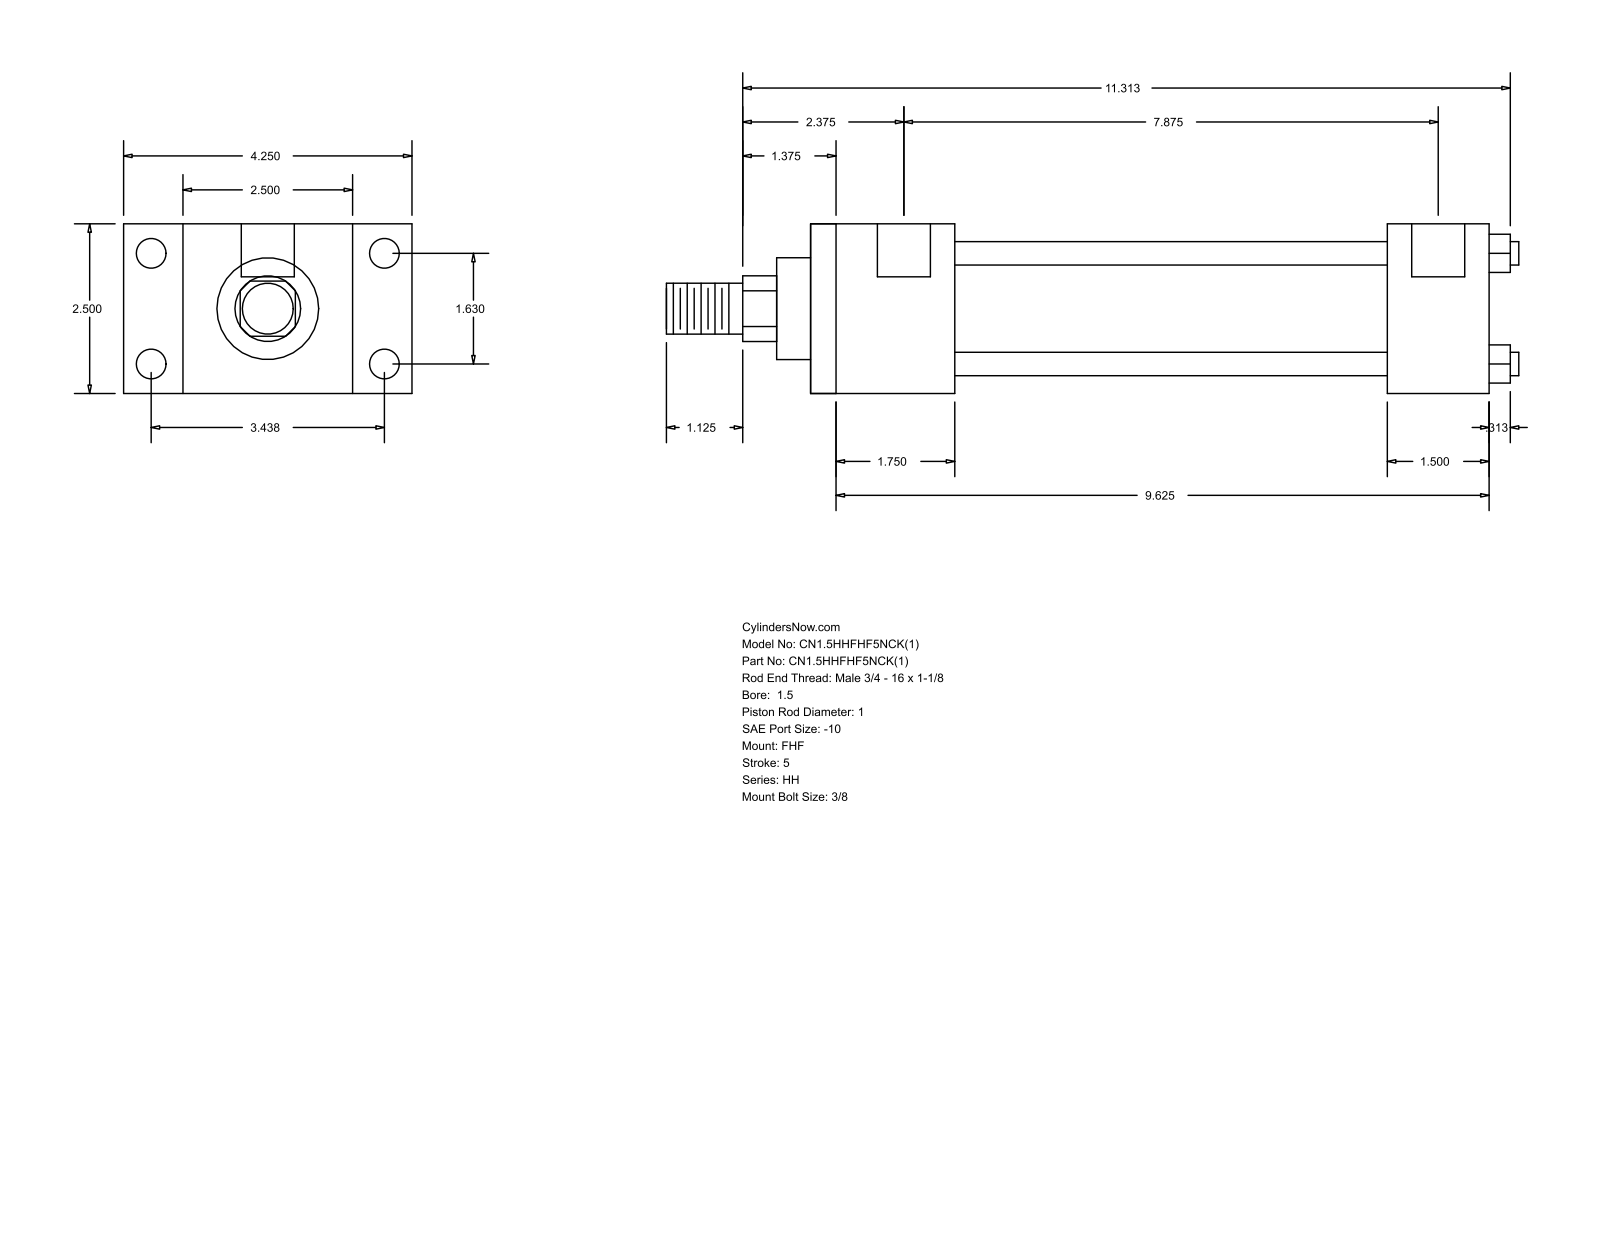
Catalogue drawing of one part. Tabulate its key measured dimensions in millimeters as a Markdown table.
| quantity | value |
| --- | --- |
| part name | HH_FHF__0150_1 |
| STEP written by | GSSL Pune (CONFIG_CONTROL_DESIGN) |
| units | millimeters |
| bodies | 0 solids, 88 faces (60 planar, 28 cylindrical, 0 other) |
| overall size | 319.09 × 107.95 × 63.5 |
| round holes (diameter × count) | 5.56 × 4, 11.13 × 4, 19.84 × 2 |
| round bosses / shafts (diameter × count) | 8.76 × 4, 44.45 × 1, 38.1 × 1, 25.4 × 1, 19.05 × 1 |
| partial cylindrical surfaces (radius × count) | 12.29 × 1 |
| main face-to-face distances | 63.5, 22.23, 85.73, 53.98, 107.96, 254, 200.02, 38.1, 215.9, 161.92 |
| hole center spacings | 1.59, 41.4, 87.32, 96.64, 201.61, 203.2, 200.02 |
